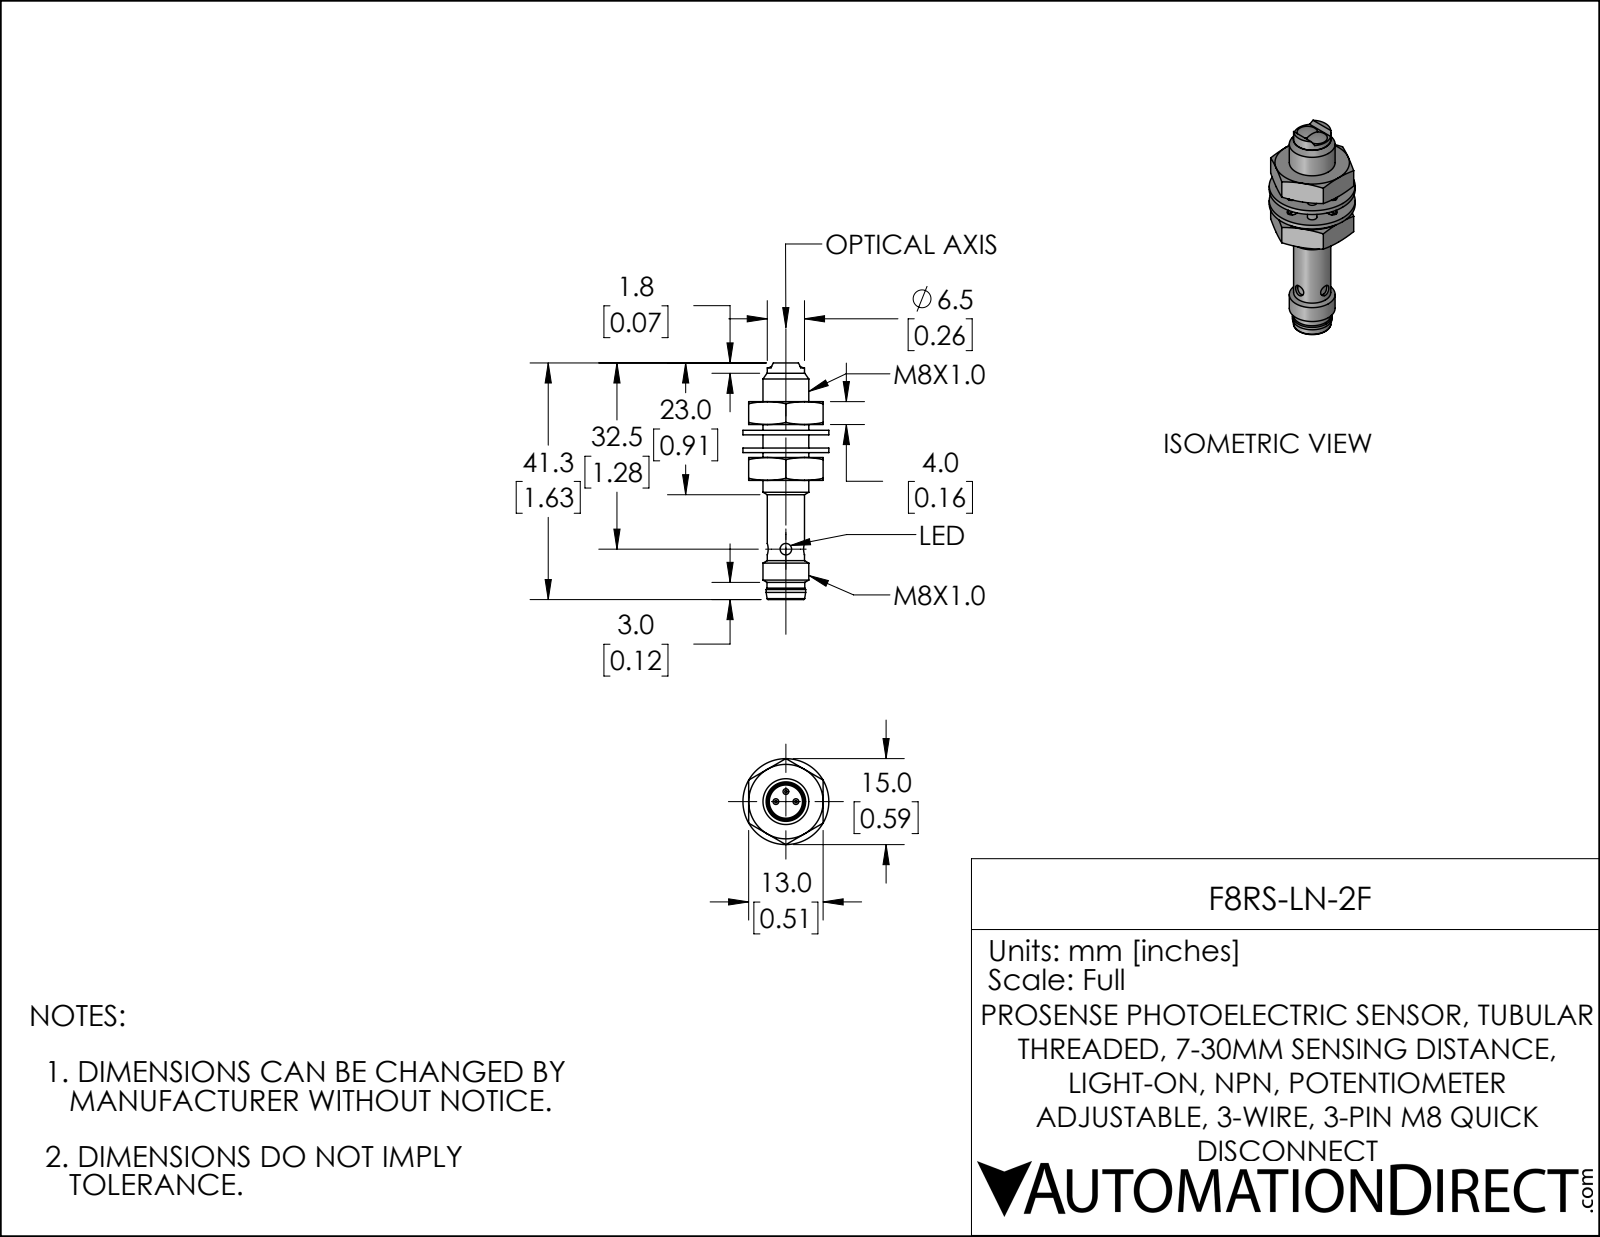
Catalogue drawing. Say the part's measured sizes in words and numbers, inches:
The part is named "F8RS-LN-2F". Its 3-D file was written by "SolidWorks 2019 (CONFIG_CONTROL_DESIGN)". It is 5 solids with 157 faces: 63 planar, 54 cylindrical and 40 other. Overall it measures 1.626 by 0.591 by 0.591 inches. Its volume is 0.162 cubic inches and its surface area 4.169 square inches. Round holes: 2 of diameter 0.079, 1 of diameter 0.228, 1 of diameter 0.272. Round bosses or shafts: 3 of diameter 0.039, 1 of diameter 0.591, 1 of diameter 0.315, 1 of diameter 0.272, 1 of diameter 0.26, 1 of diameter 0.256. Partial cylindrical surfaces (rounded edges, fillets, slot ends): 8 of radius 0.032, 1 of radius 0.109, 1 of radius 0.165. The main face-to-face distances are 0.122, 0.031, 0.512, 0.384, 0.157, 0.154, 0.091, 0.033, 0.065, 0.197.
